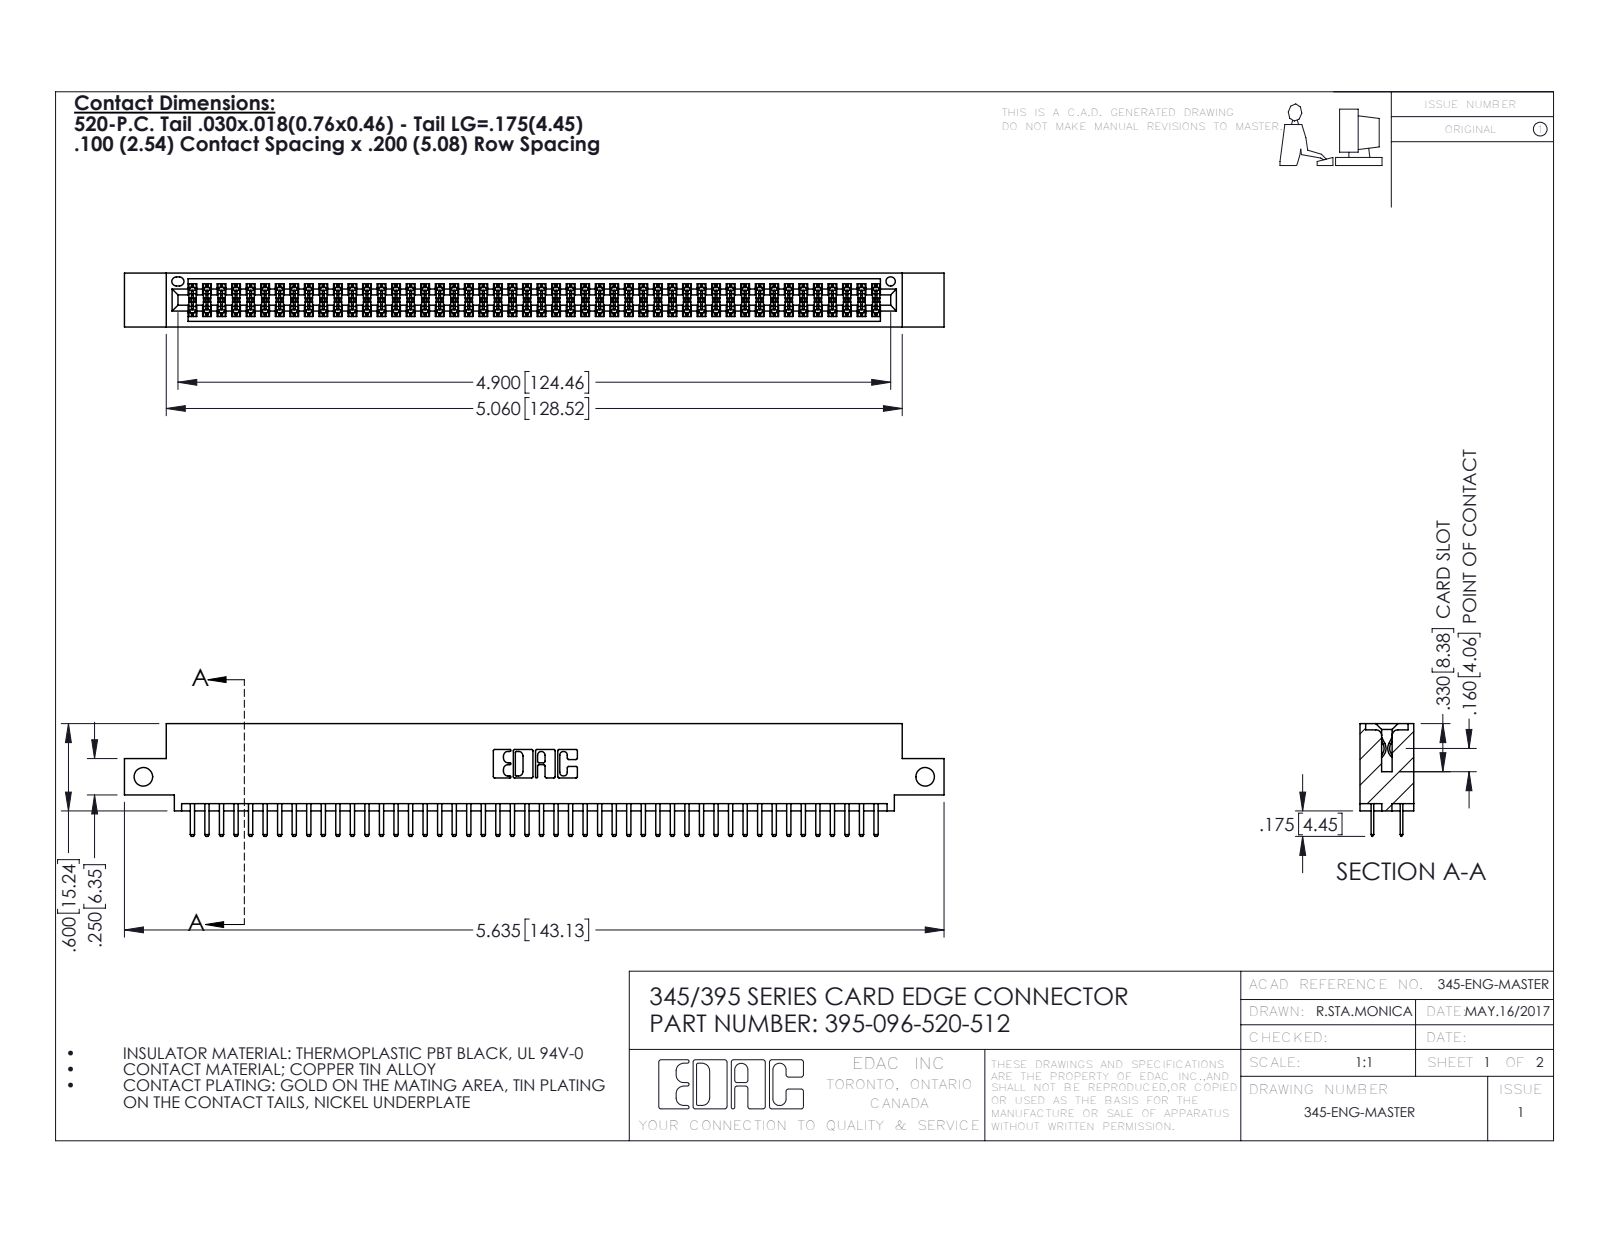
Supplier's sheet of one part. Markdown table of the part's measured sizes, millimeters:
| quantity | value |
| --- | --- |
| part name | 395-096-520-512; 345-292-001_345-293-120; 345 Part_0.110 Offset - Side Mount |
| STEP written by | SolidWorks 2016 (CONFIG_CONTROL_DESIGN) |
| units | millimeters |
| bodies | 97 solids, 5314 faces (3444 planar, 1870 cylindrical, 0 other) |
| overall size | 143.1 × 19.7 × 9.4 |
| volume | 13 700 mm³ |
| surface area | 20 320 mm² |
| round holes (diameter × count) | 3.3 × 2, 1.6 × 1 |
| partial cylindrical surfaces (radius × count) | 0.2 × 144, 0.3 × 100, 0.3 × 22, 0.2 × 6, 0.8 × 6, 0.7 × 3, 0.4 × 2, 0.5 × 2 |
| main face-to-face distances | 7.6, 1.8, 5.1, 9.4, 2.5, 6.9, 0.6, 5.7, 0.6, 1.8 |
| hole center spacings | 136.5 |
